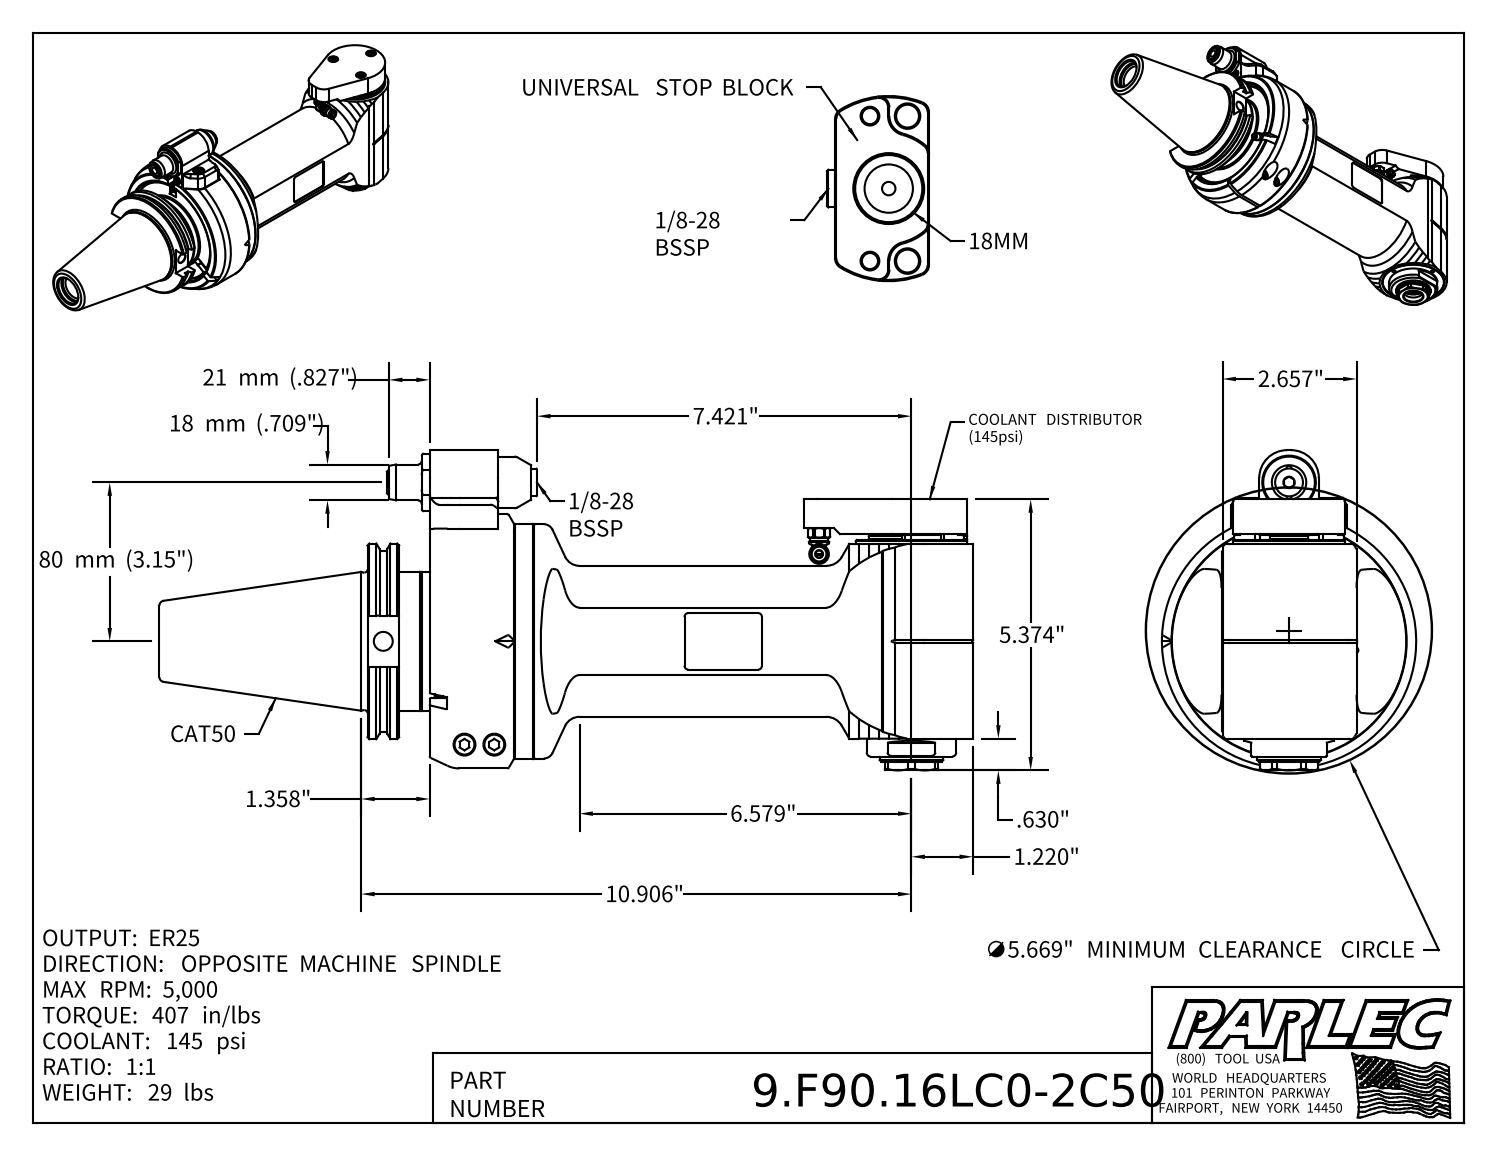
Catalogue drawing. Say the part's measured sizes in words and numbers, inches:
The part is named "9.F90.16LC0-2C50; 9_GA2_458_2 (EVO, Type 2, Cat50, 80mm); 9_F90_16LB0". Its 3-D file was written by "Autodesk Inventor 2022 (AUTOMOTIVE_DESIGN)". It is 8 solids with 787 faces: 326 planar, 201 cylindrical and 260 other. Overall it measures 16.126 by 6.348 by 5.039 inches. Its volume is 135.5 cubic inches and its surface area 391.9 square inches. Round holes: 20 of diameter 0.413, 4 of diameter 0.126, 4 of diameter 0.197, 3 of diameter 0.354, 2 of diameter 0.102, 2 of diameter 0.138, 2 of diameter 0.165, 2 of diameter 0.209, 2 of diameter 0.315, 2 of diameter 0.409, 2 of diameter 0.433, 2 of diameter 0.492. Round bosses or shafts: 5 of diameter 0.394, 4 of diameter 0.236, 3 of diameter 0.335, 2 of diameter 0.709, 2 of diameter 0.098, 1 of diameter 5.039, 1 of diameter 4.661, 1 of diameter 4.646. Partial cylindrical surfaces (rounded edges, fillets, slot ends): 13 of radius 0.079, 6 of radius 0.039, 4 of radius 0.02, 4 of radius 0.138, 4 of radius 0.157, 3 of radius 0.006, 2 of radius 0.016, 2 of radius 0.315. The main face-to-face distances are 1.378, 0.02, 2.677, 0.197, 0.236, 1.398, 1.339, 0.118, 0.581, 1.575. The hole center spacings are 1.841, 2.215, 2.603, 3.645, 3.681, 1.785, 3.22, 0.512.
